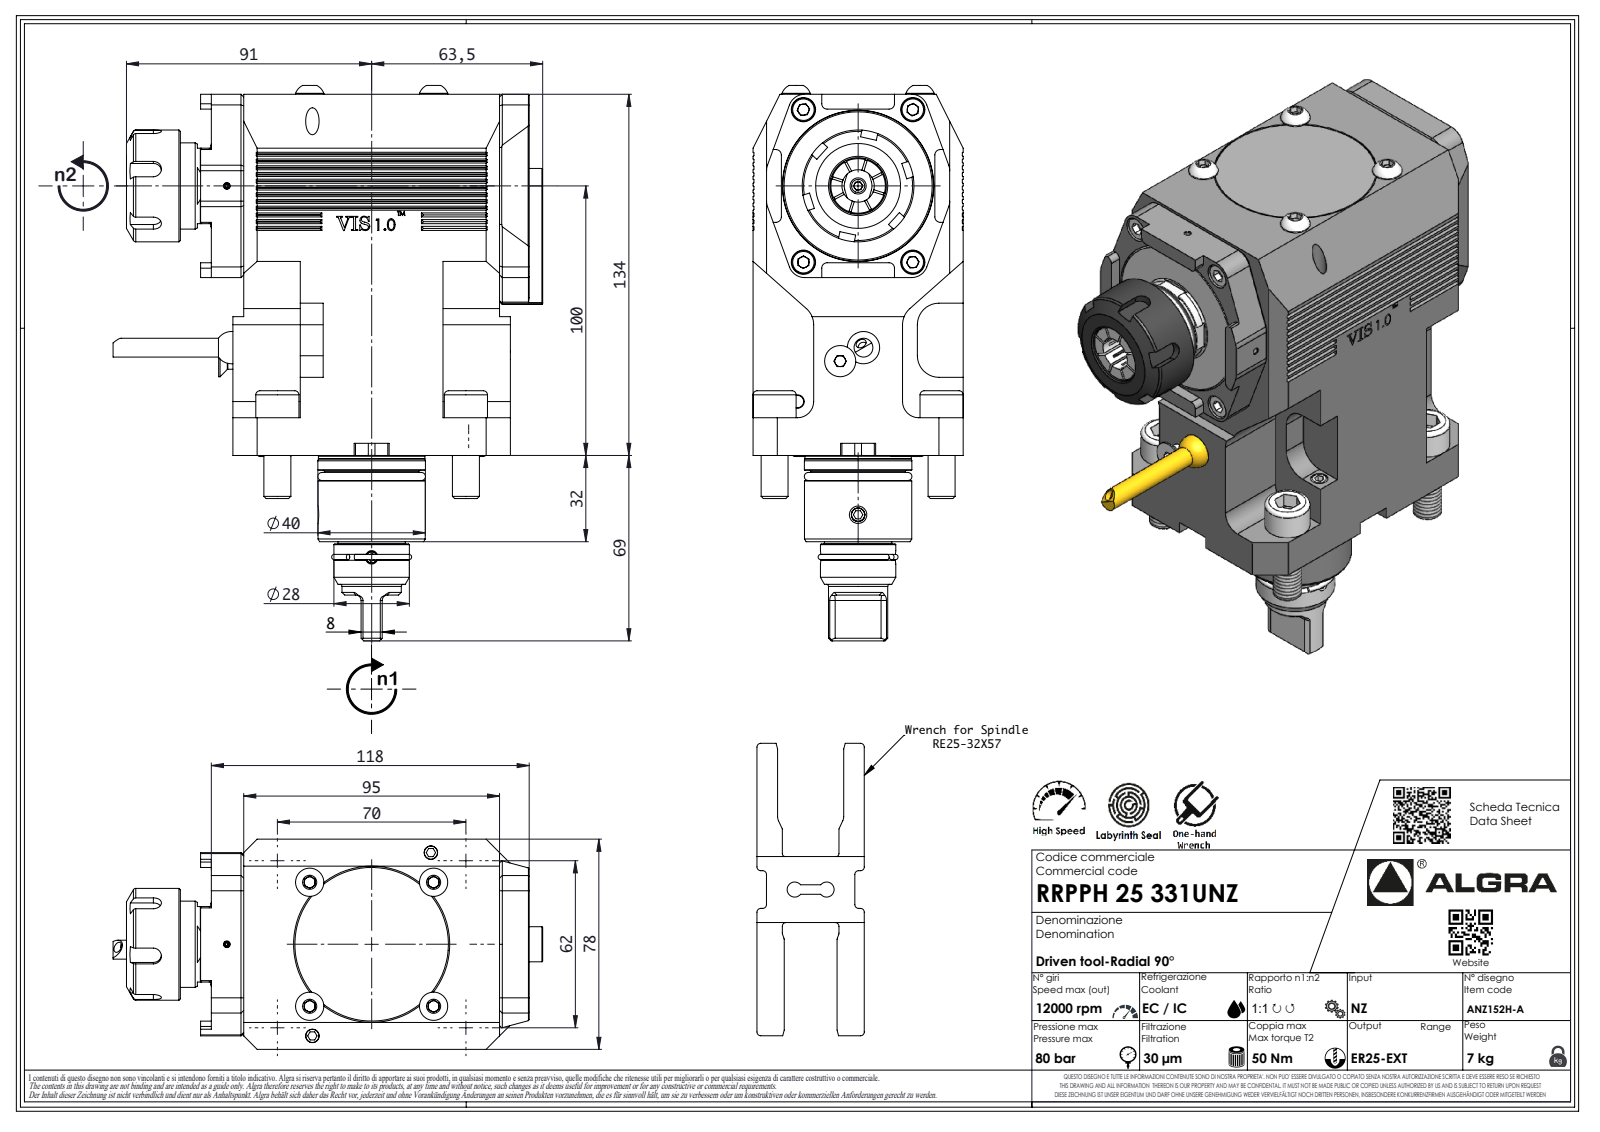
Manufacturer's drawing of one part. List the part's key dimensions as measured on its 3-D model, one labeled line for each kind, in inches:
Part name (STEP PRODUCT): RRPPH25331UNZ
STEP written by: SolidWorks 2023 (AUTOMOTIVE_DESIGN)
Units: inches
Bodies: 1 solid, 641 faces (386 planar, 114 cylindrical, 141 other)
Overall size (bounding box): 7.984 × 6.084 × 3.071
Volume: 67.74 in³ · Surface area: 138.6 in²
Round holes (diameter × count): ⌀0.083 ×1
Round bosses / shafts (diameter × count): ⌀0.63 ×3, ⌀0.394 ×3, ⌀1.634 ×1, ⌀1.571 ×1, ⌀1.567 ×1, ⌀1.555 ×1, ⌀1.382 ×1, ⌀1.26 ×1
Partial cylindrical surfaces — rounded edges, fillets, slot ends (radius × count): R0.197 ×16, R0.079 ×14, R0.236 ×10, R0.013 ×7, R0.02 ×7, R0.146 ×7, R0.118 ×6, R0.315 ×6
Main face-to-face distances: 3.071, 5.276, 0.157, 3.898, 0.472, 4.37, 0.886, 1.299, 0.984, 0.827
